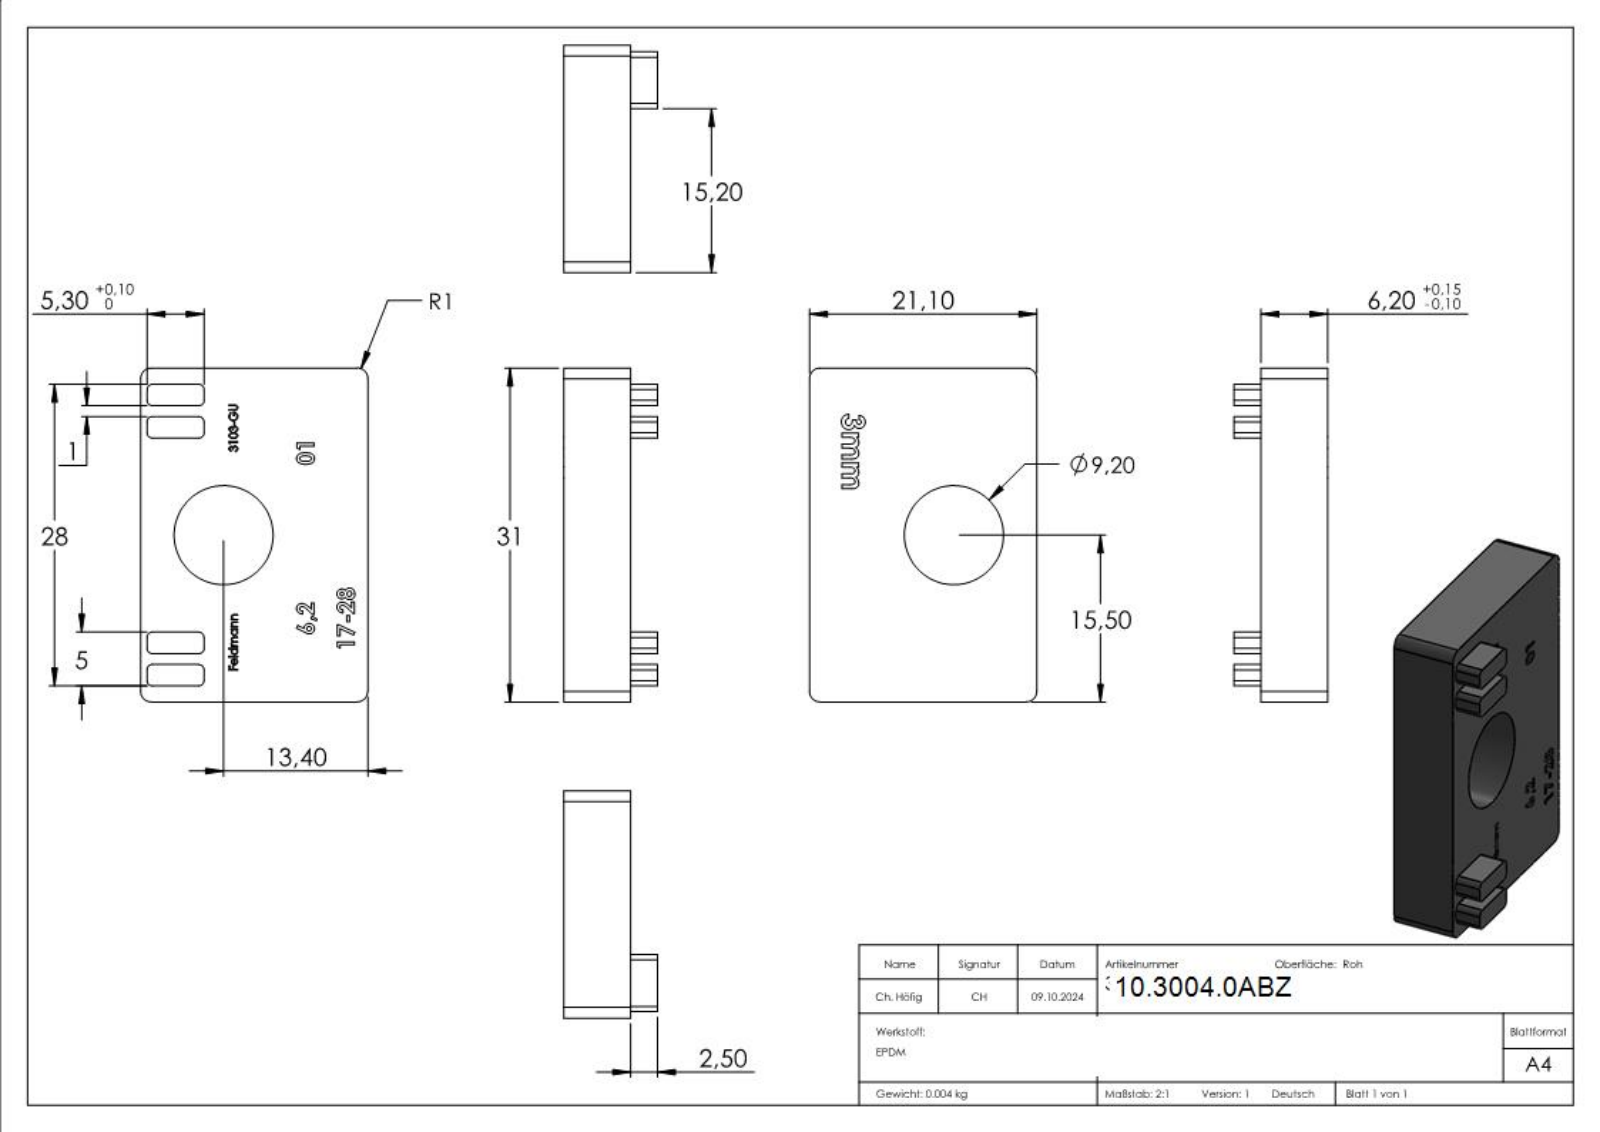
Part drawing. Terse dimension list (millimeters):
name: 3103-GU
written by: SolidWorks 2018 (CONFIG_CONTROL_DESIGN)
unit: mm
bodies: 1 solid, 408 faces (211 planar, 21 cylindrical, 176 other)
size: 31 × 21.1 × 8.7
volume: 3 740 mm³; area: 2 139 mm²
holes: 1× ⌀9.2
rounds: 16× R0.5, 4× R1
face distances: 6.2, 21.1, 31, 3, 2, 23, 8.7, 2.5, 5, 1.5
